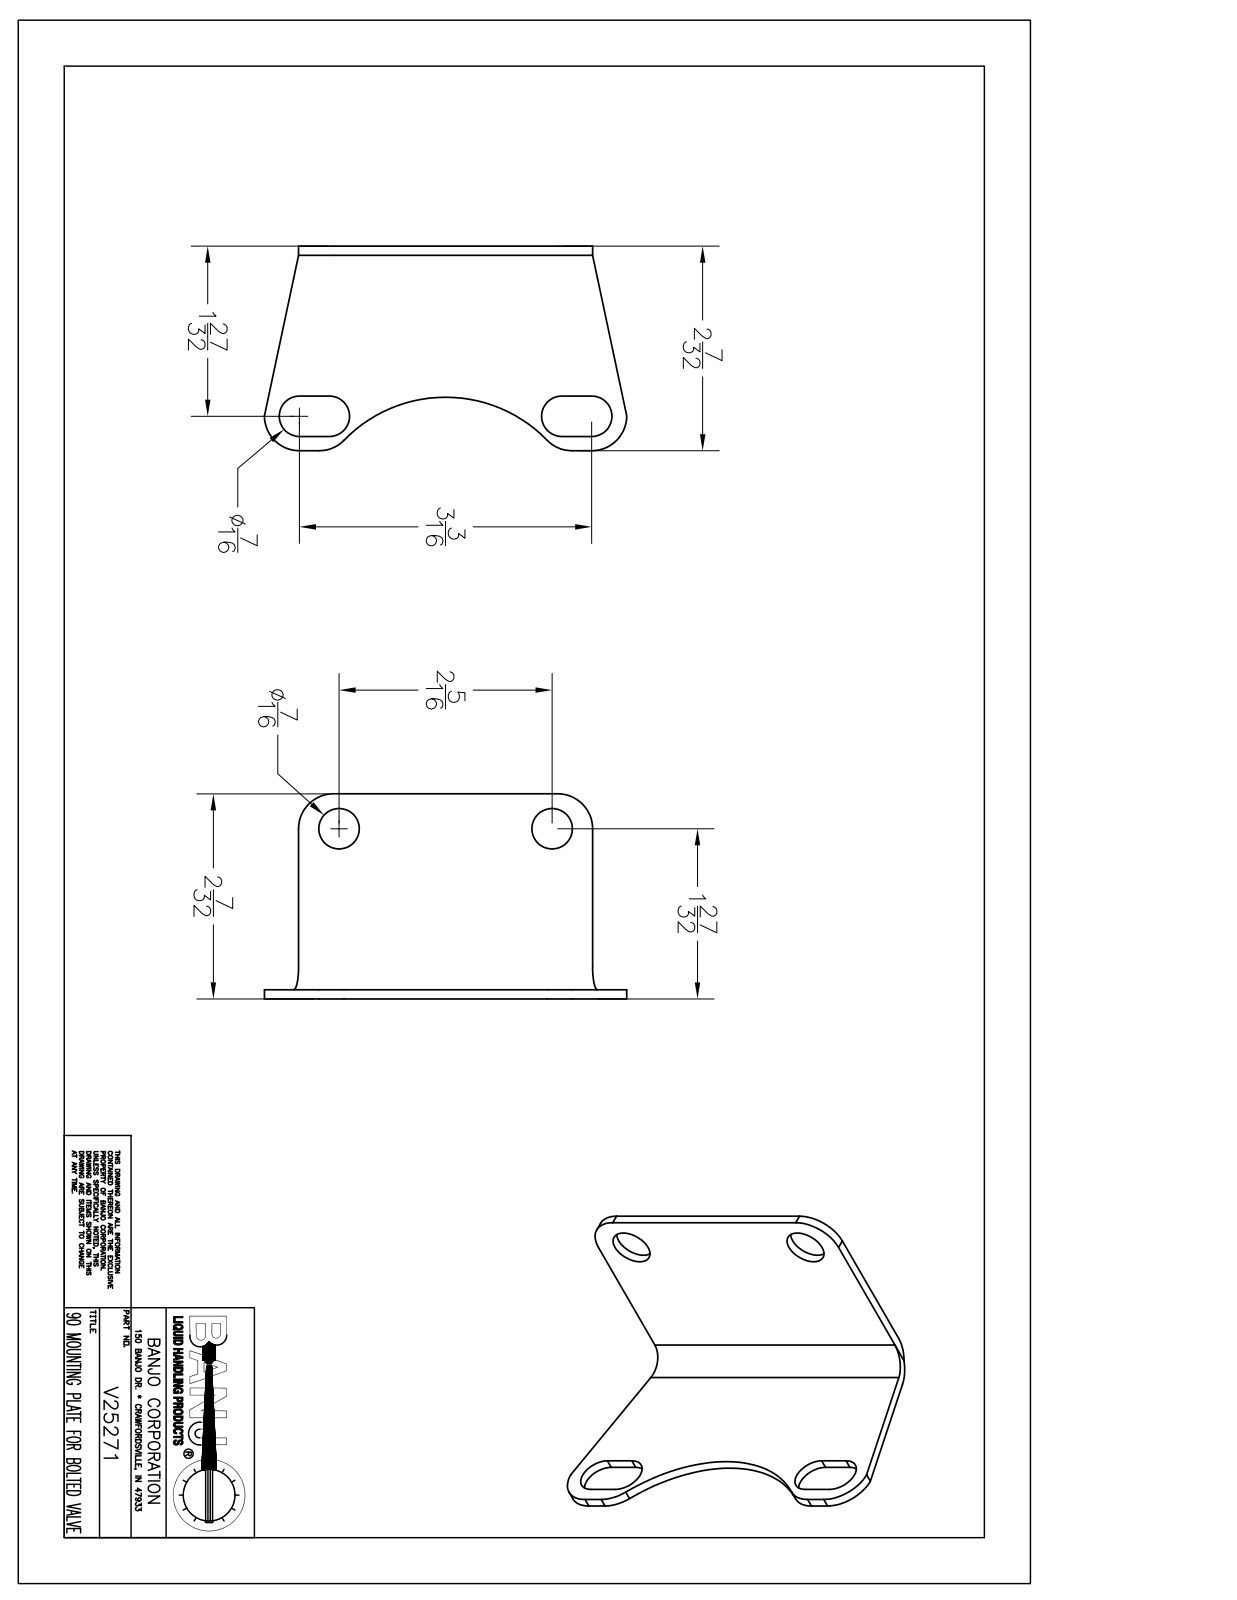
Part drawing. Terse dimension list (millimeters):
name: V25271
written by: Autodesk Inventor 2014 (AUTOMOTIVE_DESIGN)
unit: mm
bodies: 1 solid, 368 faces (181 planar, 15 cylindrical, 172 other)
size: 99.75 × 56.52 × 56.52
volume: 20 368 mm³; area: 17 593 mm²
holes: 2× ⌀11.18
rounds: 6× R9.53, 4× R5.59, 1× R6.35, 1× R8.89, 1× R39.01
face distances: 2.54, 53.98, 56.52, 81.28, 2.29, 54.23, 41.4, 52.58, 38.86, 50.04
hole spacings: 57.48
